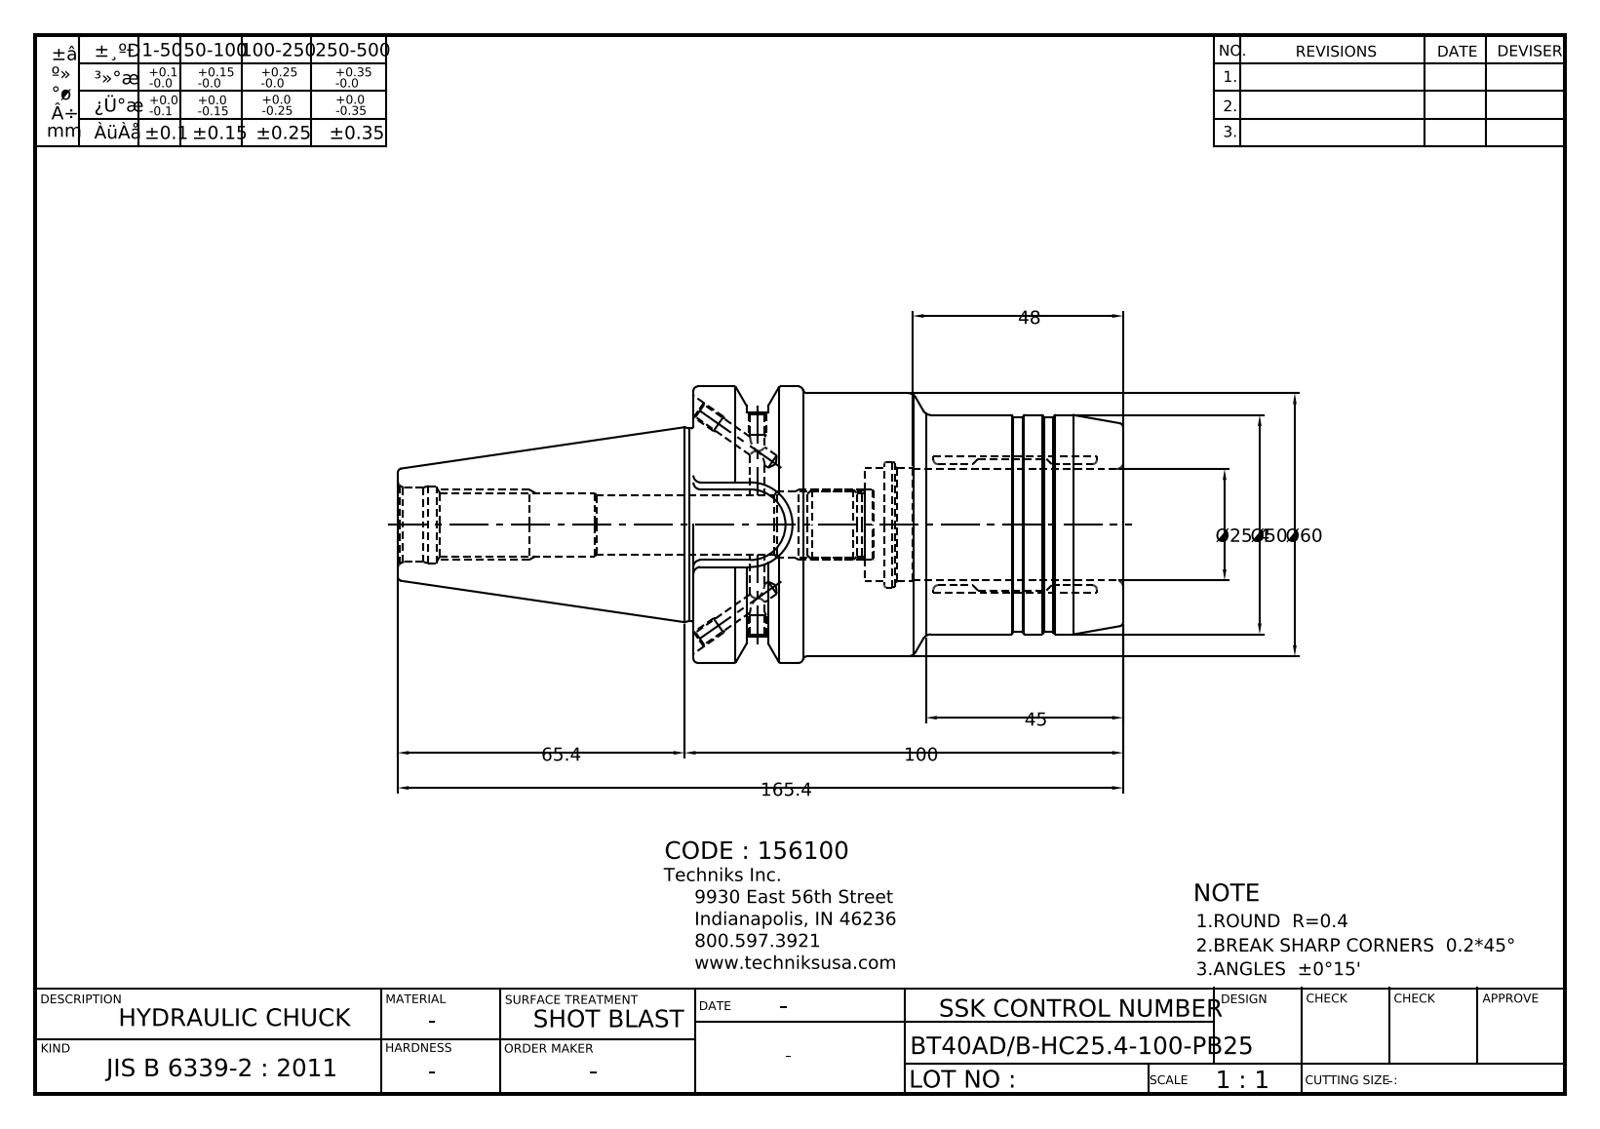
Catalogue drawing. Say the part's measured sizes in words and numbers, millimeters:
The part is named "LO-BT40ADB-HC25.4-100". Its 3-D file was written by "Autodesk Inventor 2020 (AUTOMOTIVE_DESIGN)". It is 1 solid with 89 faces: 20 planar, 33 cylindrical and 36 other. Overall it measures 155.4 by 63 by 63 millimeters. Its volume is 223 355 cubic millimeters and its surface area 37 903 square millimeters. Round holes: 4 of diameter 3.24, 4 of diameter 4, 1 of diameter 13.5, 1 of diameter 13.84, 1 of diameter 14.92, 1 of diameter 17, 1 of diameter 17.6, 1 of diameter 25.4, 1 of diameter 25.8. Round bosses or shafts: 1 of diameter 63, 1 of diameter 60, 1 of diameter 51, 1 of diameter 50, 1 of diameter 49, 1 of diameter 44. Partial cylindrical surfaces (rounded edges, fillets, slot ends): 1 of radius 8.05. The main face-to-face distances are 88, 29, 59, 45.2, 17.1, 11.9, 70.9, 12.1, 5, 16.9.
